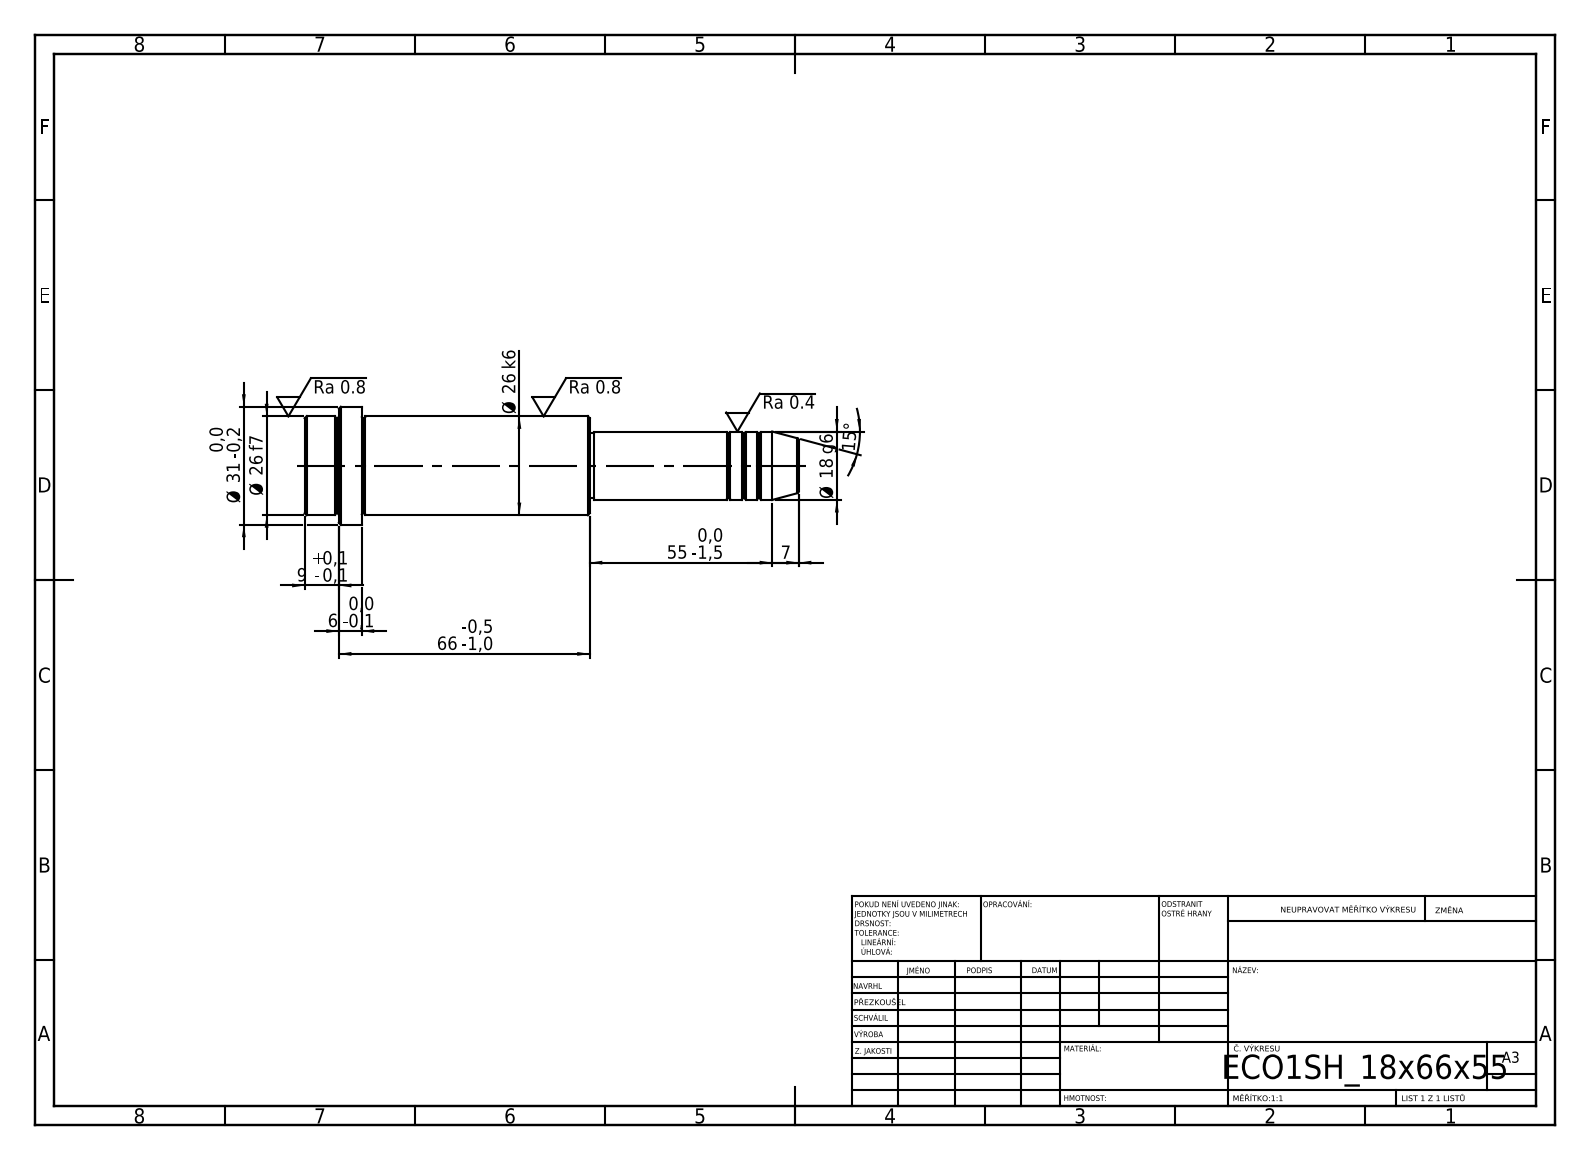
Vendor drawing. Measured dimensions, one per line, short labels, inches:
written by: SolidWorks 2019 (CONFIG_CONTROL_DESIGN)
unit: in
bodies: 1 solid, 52 faces (6 planar, 16 cylindrical, 30 other)
size: 5.118 × 1.22 × 1.22
volume: 3.333 in³; area: 16.83 in²
bosses: 1× ⌀1.22, 1× ⌀1.024, 1× ⌀0.709, 1× ⌀0.669
face distances: 2.953, 2.362, 0.591, 2.598, 0.236, 0.354, 2.165, 4.528, 4.764, 5.118
